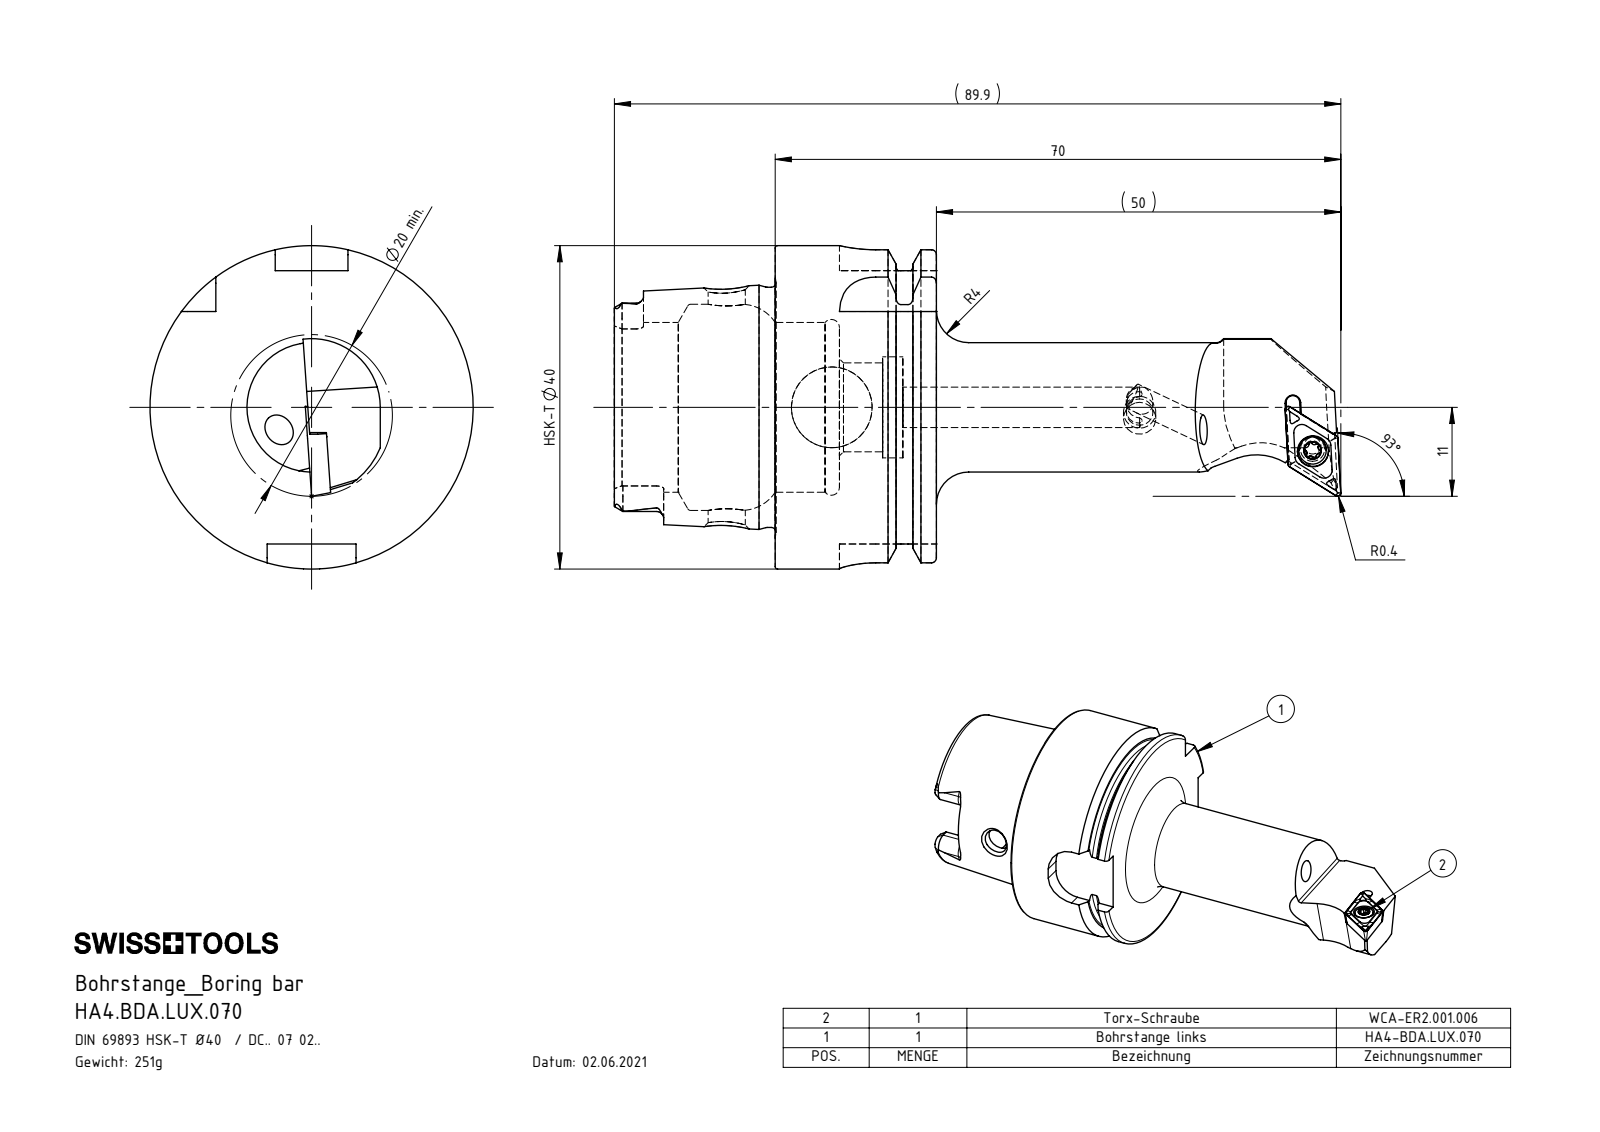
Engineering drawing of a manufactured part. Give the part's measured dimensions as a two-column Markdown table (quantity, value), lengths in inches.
| quantity | value |
| --- | --- |
| part name | KVT_MB_600_040; DCMT070204; HA4.BDA.LUX.070; WCA-ER2.001.006_A (+1 more) |
| STEP written by | SolidWorks 2017 (AUTOMOTIVE_DESIGN) |
| units | inches |
| bodies | 5 solids, 238 faces (82 planar, 62 cylindrical, 94 other) |
| overall size | 3.539 × 1.575 × 1.575 |
| volume | 1.95 in³ |
| surface area | 19.85 in² |
| round holes (diameter × count) | 0.13 × 2, 0.081 × 1, 0.11 × 1, 0.118 × 1, 0.152 × 1, 0.157 × 1, 0.181 × 1, 0.197 × 1, 0.394 × 1, 0.433 × 1, 0.492 × 1, 0.827 × 1 |
| round bosses / shafts (diameter × count) | 1.575 × 1, 1.368 × 1, 1.17 × 1, 0.63 × 1, 0.157 × 1, 0.134 × 1, 0.098 × 1 |
| partial cylindrical surfaces (radius × count) | 0.008 × 6, 0.035 × 6, 0.074 × 4, 0.177 × 4, 0.014 × 3, 0.014 × 3, 0.02 × 1, 0.033 × 1 |
| main face-to-face distances | 0.785, 0.313, 0.472, 0.783, 1.096, 1.569, 1.406, 0.622, 0.309, 0.163 |
